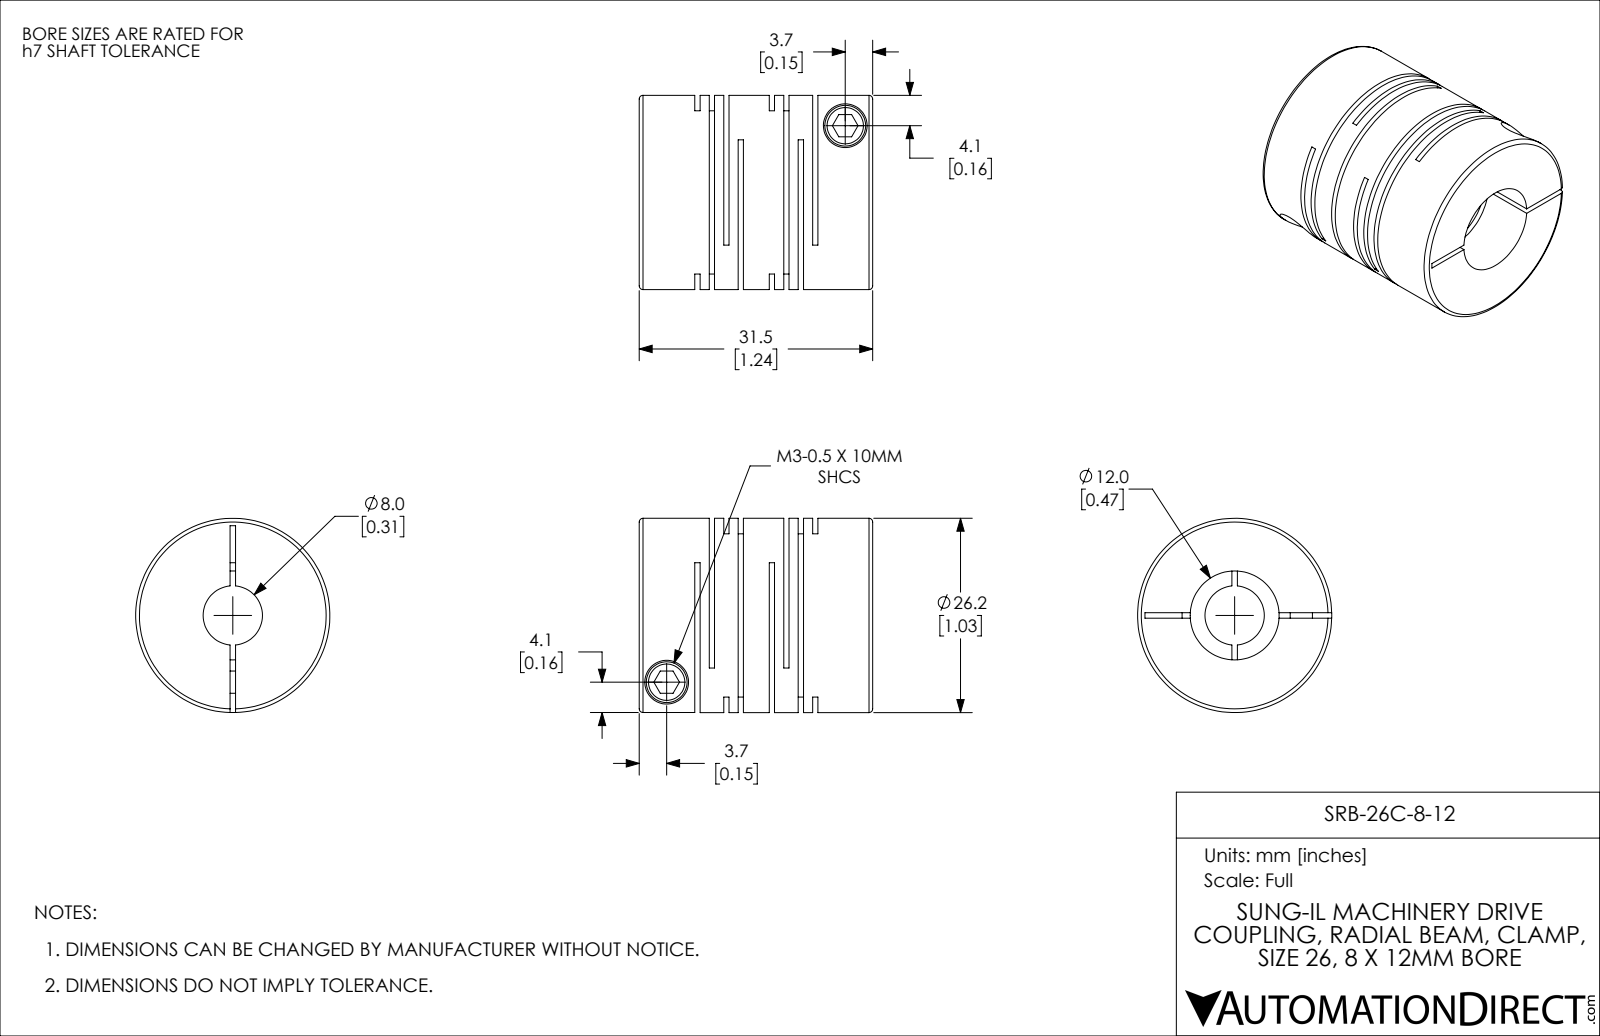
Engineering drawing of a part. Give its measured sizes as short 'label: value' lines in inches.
name: SRB-26C-8-12
written by: SolidWorks 2021 (CONFIG_CONTROL_DESIGN)
unit: in
bodies: 1 solid, 114 faces (60 planar, 42 cylindrical, 12 other)
size: 1.24 × 1.031 × 1.031
volume: 0.703 in³; area: 15.96 in²
holes: 2× ⌀0.118, 2× ⌀0.232, 1× ⌀0.315, 1× ⌀0.472
bosses: 2× ⌀0.217, 1× ⌀1.031
face distances: 0.077, 0.396, 0.028, 0.154, 0.319, 0.472, 0.049, 0.105, 0.368, 0.549
